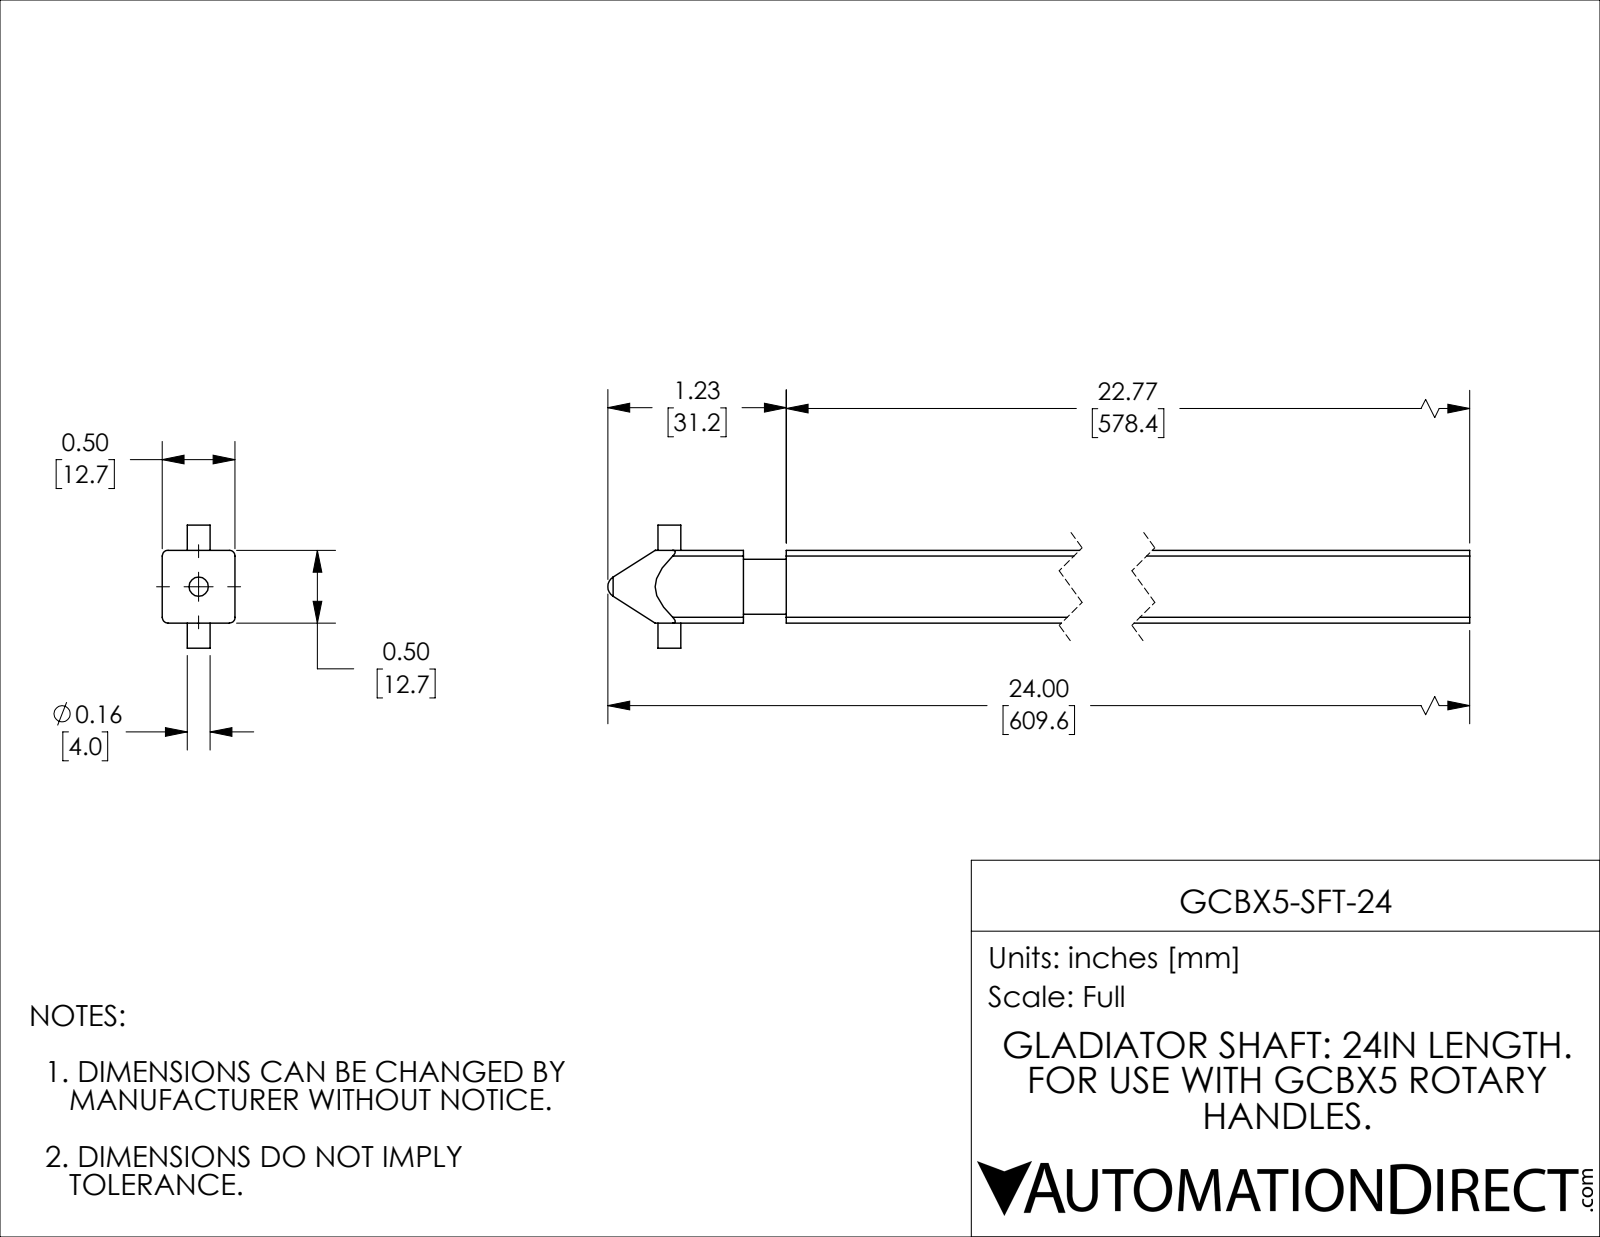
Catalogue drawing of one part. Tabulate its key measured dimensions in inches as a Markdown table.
| quantity | value |
| --- | --- |
| part name | GCBX5-SFT-24 |
| STEP written by | SolidWorks 2021 (CONFIG_CONTROL_DESIGN) |
| units | inches |
| bodies | 1 solid, 39 faces (15 planar, 17 cylindrical, 7 other) |
| overall size | 23.999 × 0.846 × 0.5 |
| volume | 5.863 in³ |
| surface area | 46.95 in² |
| round holes (diameter × count) | 0.142 × 1 |
| round bosses / shafts (diameter × count) | 0.378 × 1, 0.157 × 1 |
| partial cylindrical surfaces (radius × count) | 0.039 × 4 |
| main face-to-face distances | 0.5, 22.773, 23.068, 0.295, 0.244, 0.256, 0.173, 0.673, 0.846 |
